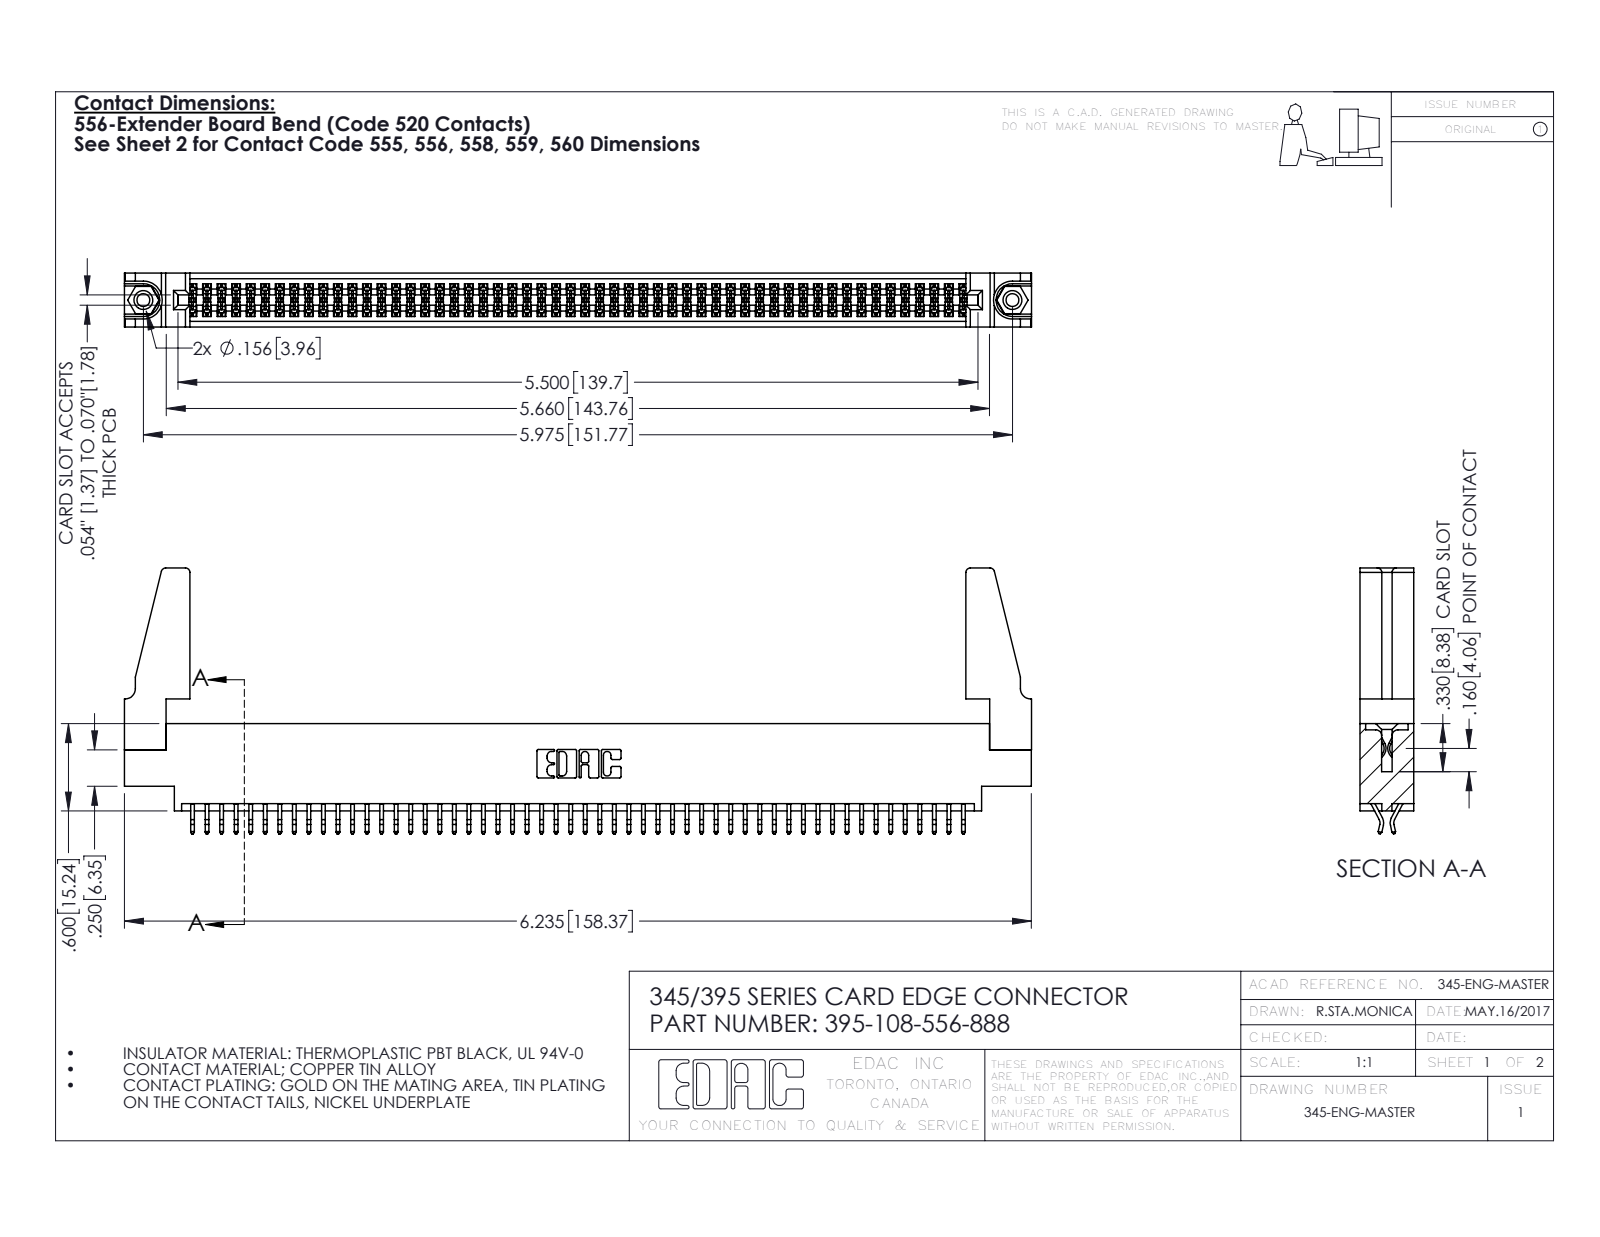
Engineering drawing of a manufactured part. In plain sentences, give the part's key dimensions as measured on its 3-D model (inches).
The part is named "345 Part_0.170 Offset - 0.156 Dia-TH; 395-108-556-888; 345-220-078_345-220-088; 345-250-001_345-250-001-102 (+1 more)". Its 3-D file was written by "SolidWorks 2016 (CONFIG_CONTROL_DESIGN)". It is 113 solids with 6302 faces: 4152 planar, 2134 cylindrical and 16 other. Overall it measures 6.236 by 1.827 by 0.37 inches. Its volume is 1.137 cubic inches and its surface area 40.51 square inches. Round holes: 2 of diameter 0.089, 2 of diameter 0.125, 2 of diameter 0.156, 1 of diameter 0.064. Round bosses or shafts: 2 of diameter 0.155. Partial cylindrical surfaces (rounded edges, fillets, slot ends): 162 of radius 0.006, 22 of radius 0.01, 8 of radius 0.03, 6 of radius 0.007, 6 of radius 0.031, 3 of radius 0.026, 2 of radius 0.01, 2 of radius 0.014. The main face-to-face distances are 0.072, 0.298, 0.37, 0.025, 0.2, 0.098, 0.272, 0.225, 0.175, 0.149. The hole center spacings are 0.27, 5.739, 5.975.
